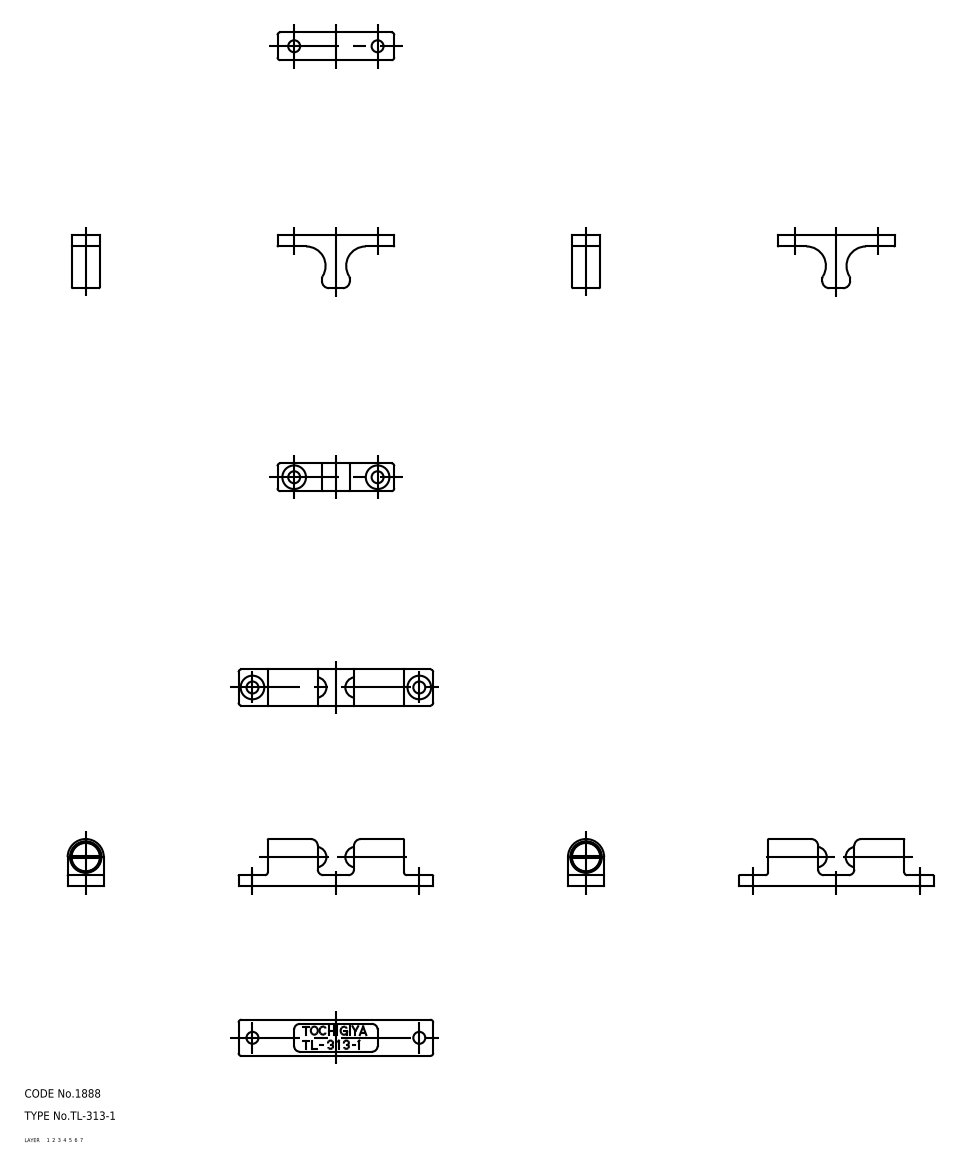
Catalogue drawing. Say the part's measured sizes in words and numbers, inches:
The part is named "67114046; 67114059; 67114072; 67114085 (+2 more)". Its 3-D file was written by "CADfix (AUTOMOTIVE_DESIGN)". It is 6 solids with 92 faces: 0 planar, 0 cylindrical and 92 other. Overall it measures 2.77 by 2.756 by 0.512 inches. Its volume is 0.694 cubic inches and its surface area 12.87 square inches.
